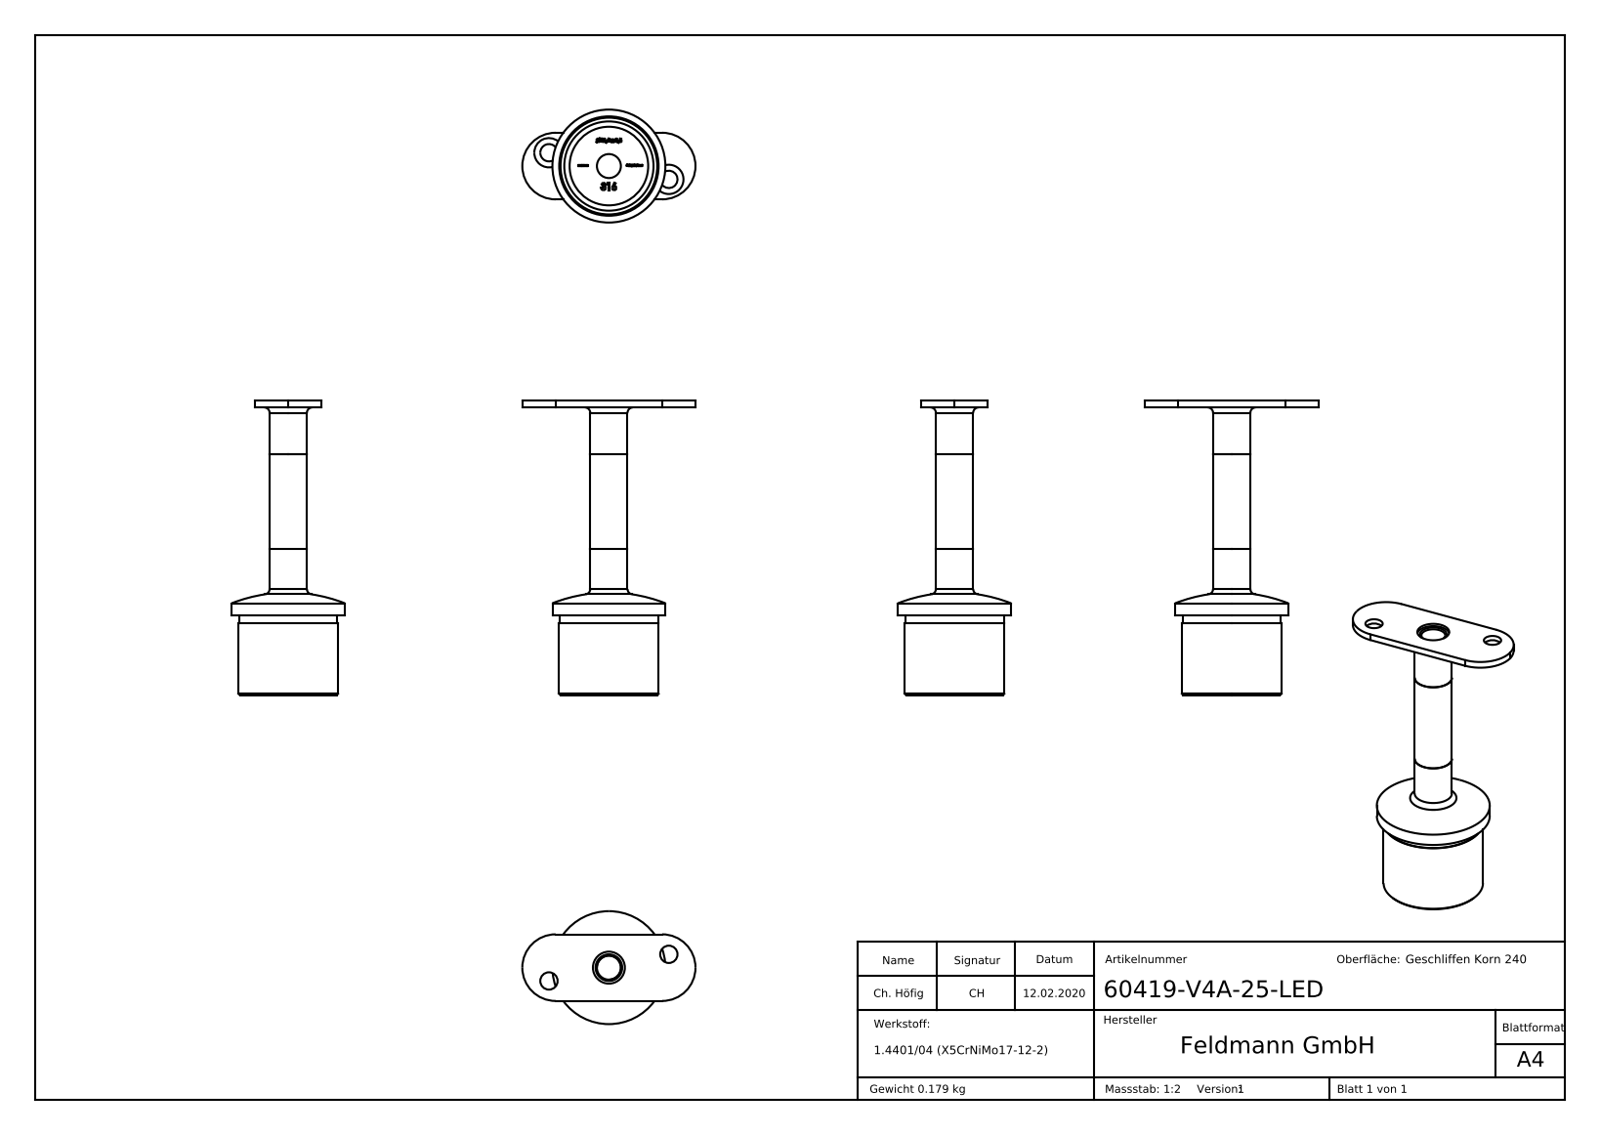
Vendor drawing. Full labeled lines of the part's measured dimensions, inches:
Part name (STEP PRODUCT): 604XX-XXX-LED Teil3; 60419-V4A-25-LED; 604XX-XXX-LED Teil1; Kabel (+4 more)
STEP written by: SolidWorks 2015 (CONFIG_CONTROL_DESIGN)
Units: inches
Bodies: 349 solids, 1449 faces (815 planar, 435 cylindrical, 199 other)
Overall size (bounding box): 6.567 × 2.558 × 1.669
Volume: 1.41 in³ · Surface area: 33.26 in²
Round holes (diameter × count): ⌀0.256 ×2, ⌀0.433 ×2, ⌀0.354 ×1, ⌀0.394 ×1, ⌀0.472 ×1, ⌀1.358 ×1
Round bosses / shafts (diameter × count): ⌀0.059 ×2, ⌀1.669 ×1, ⌀1.508 ×1, ⌀1.492 ×1, ⌀0.551 ×1, ⌀0.469 ×1
Partial cylindrical surfaces — rounded edges, fillets, slot ends (radius × count): R0.012 ×2, R0.098 ×2, R0.492 ×2, R0.835 ×1, R0.933 ×1
Main face-to-face distances: 0.079, 1.181, 1.26, 0.984, 3.563, 2.382, 2.303, 2.165, 0.906, 1.398
Hole centre spacings: 0.012, 0.013, 4.608, 4.6, 4.604, 4.604, 4.605, 4.611
